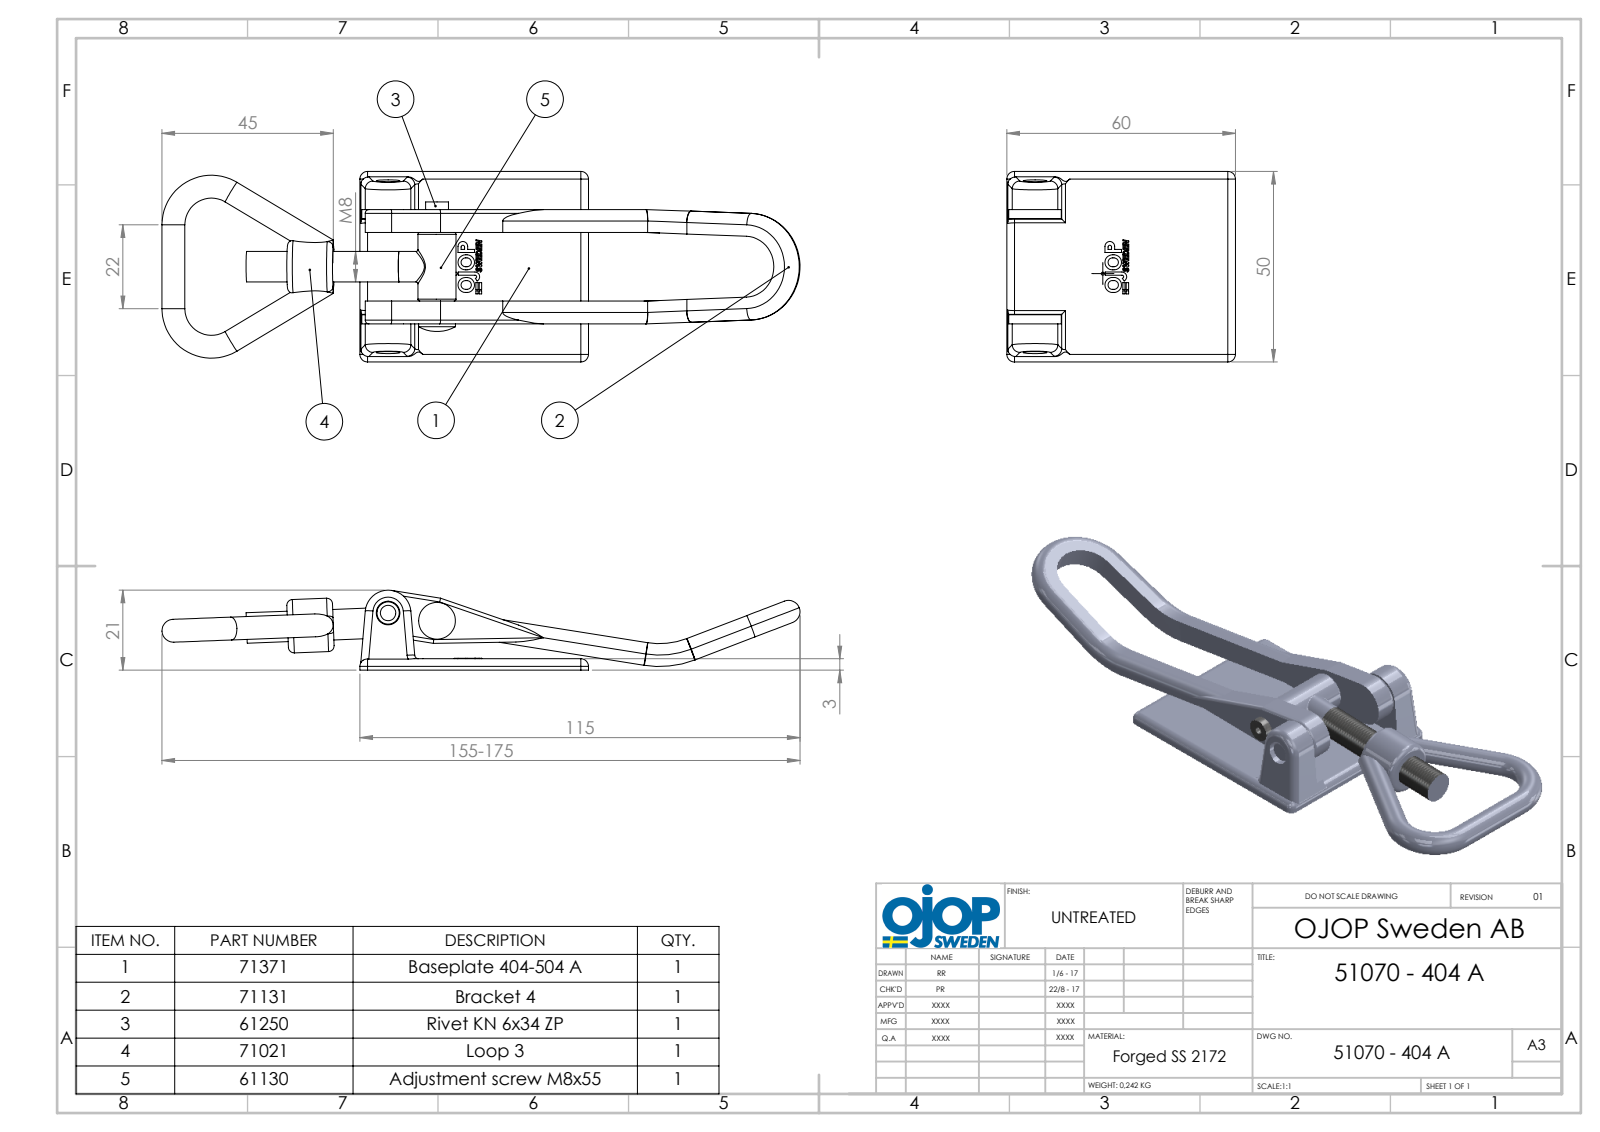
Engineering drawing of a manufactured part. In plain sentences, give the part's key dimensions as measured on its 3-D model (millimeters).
The part is named "Ring 3; 51070 - 404 A; Bygel 4; Justerskruv M8 (+2 more)". Its 3-D file was written by "SolidWorks 2015 (AUTOMOTIVE_DESIGN)". It is 5 solids with 197 faces: 57 planar, 82 cylindrical and 58 other. Overall it measures 171.48 by 50 by 21 millimeters. Its volume is 29 832 cubic millimeters and its surface area 19 922 square millimeters. Round holes: 2 of diameter 6.2, 1 of diameter 2, 1 of diameter 6.3, 1 of diameter 8.1. Round bosses or shafts: 4 of diameter 6, 1 of diameter 10, 1 of diameter 9.66, 1 of diameter 8.01, 1 of diameter 8, 1 of diameter 5.85. Partial cylindrical surfaces (rounded edges, fillets, slot ends): 18 of radius 3, 8 of radius 2, 4 of radius 1, 4 of radius 6.99, 2 of radius 1.5, 1 of radius 6, 1 of radius 8, 1 of radius 20. The main face-to-face distances are 3, 6, 18, 24, 30, 5.99, 16, 10, 34, 40. The hole center spacings are 13.
